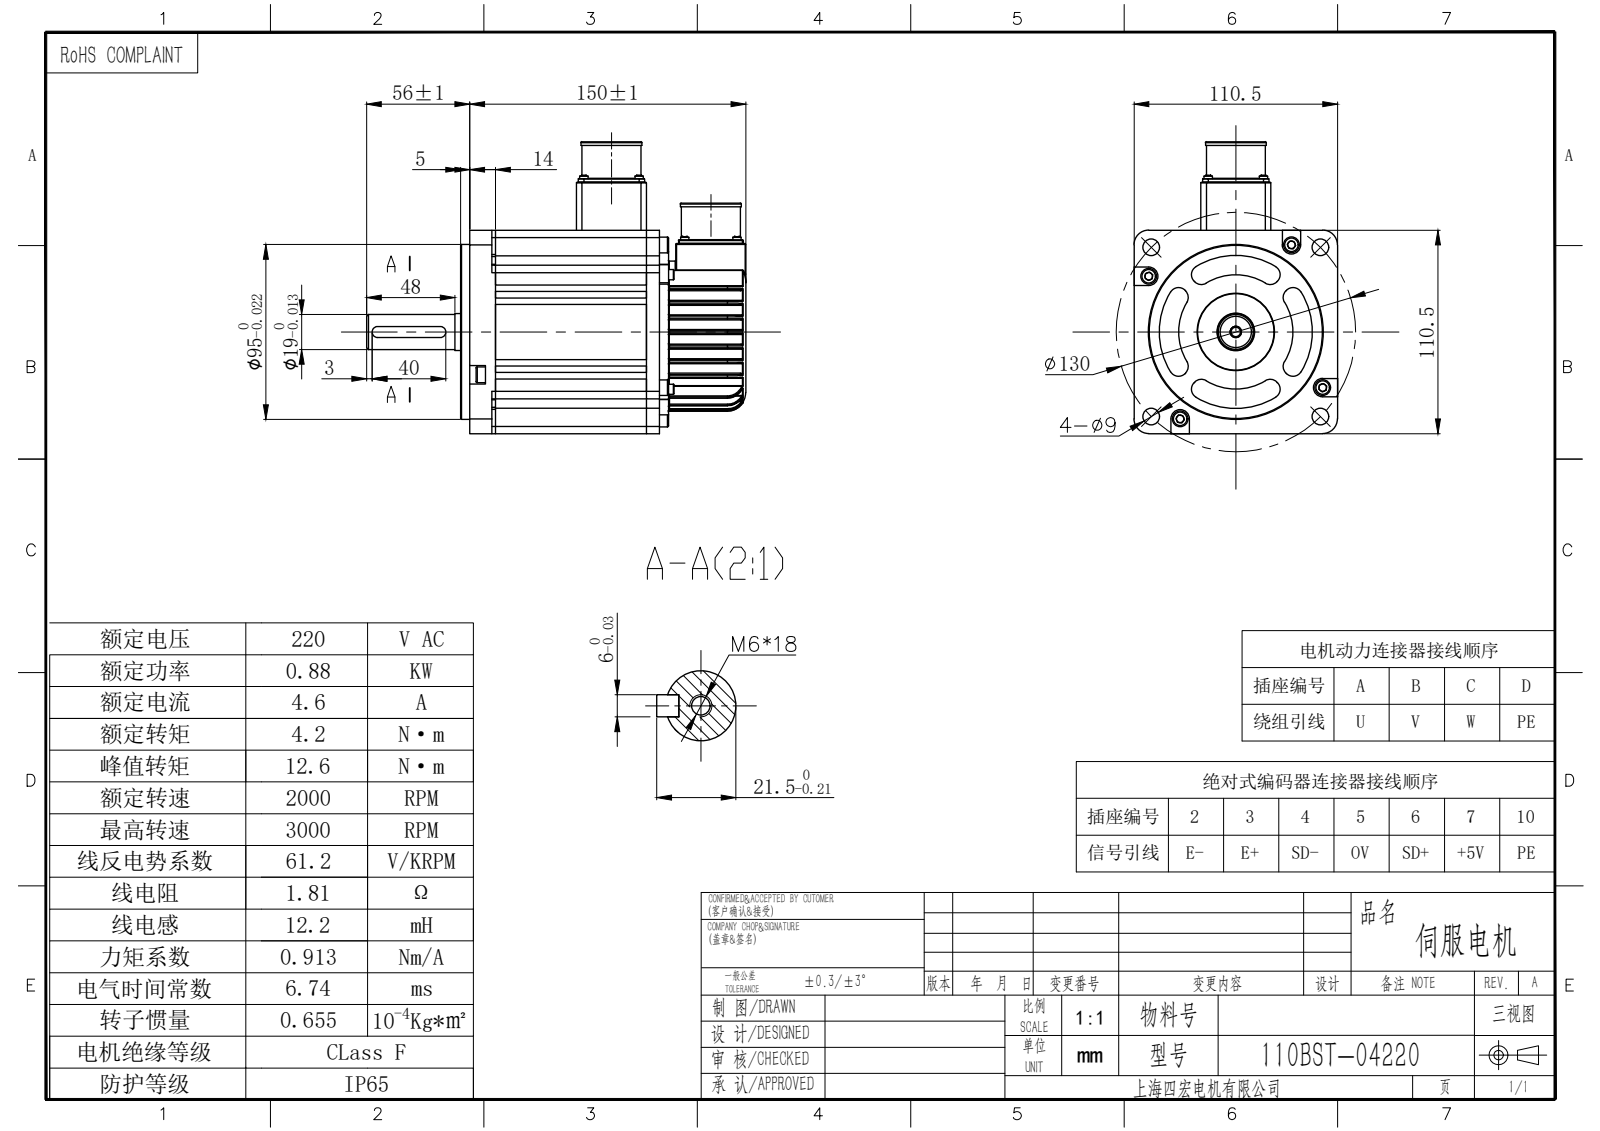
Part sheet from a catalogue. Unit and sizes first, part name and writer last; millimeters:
Units: millimetres
Overall size (bounding box): 206 × 158.5 × 110.5
Round holes (diameter × count): ⌀2.5 ×8, ⌀5 ×5, ⌀4 ×4, ⌀9 ×4, ⌀29 ×2, ⌀20 ×1, ⌀42 ×1, ⌀60 ×1, ⌀69.94 ×1
Round bosses / shafts (diameter × count): ⌀4.5 ×8, ⌀3 ×8, ⌀8.5 ×4, ⌀5.5 ×4, ⌀33 ×2, ⌀32 ×2, ⌀95 ×1, ⌀19 ×1
Partial cylindrical surfaces — rounded edges, fillets, slot ends (radius × count): R0.5 ×70, R0.4 ×60, R0.3 ×32, R5 ×20, R0.2 ×16, R3 ×10, R1 ×8, R1.5 ×8
Main face-to-face distances: 7, 82, 89, 19, 110.5, 91.5, 33.25, 96, 5, 101
Hole centre spacings: 78.49, 15.76, 20.08, 21.21, 28.4, 30, 44, 56.1
Volume: 1 118 000 mm³ · Surface area: 198 737 mm²
Bodies: 27 solids, 1492 faces (509 planar, 528 cylindrical, 455 other)
Part name (STEP PRODUCT): 110BST-M04220; 航插1; 110BST后端盖; cross recessed small pan head screws gb_GB_CROSS_SCREWS_TYPE3 M2.5X10-10-N (+7 more)
STEP written by: SolidWorks 2020 (AUTOMOTIVE_DESIGN)
